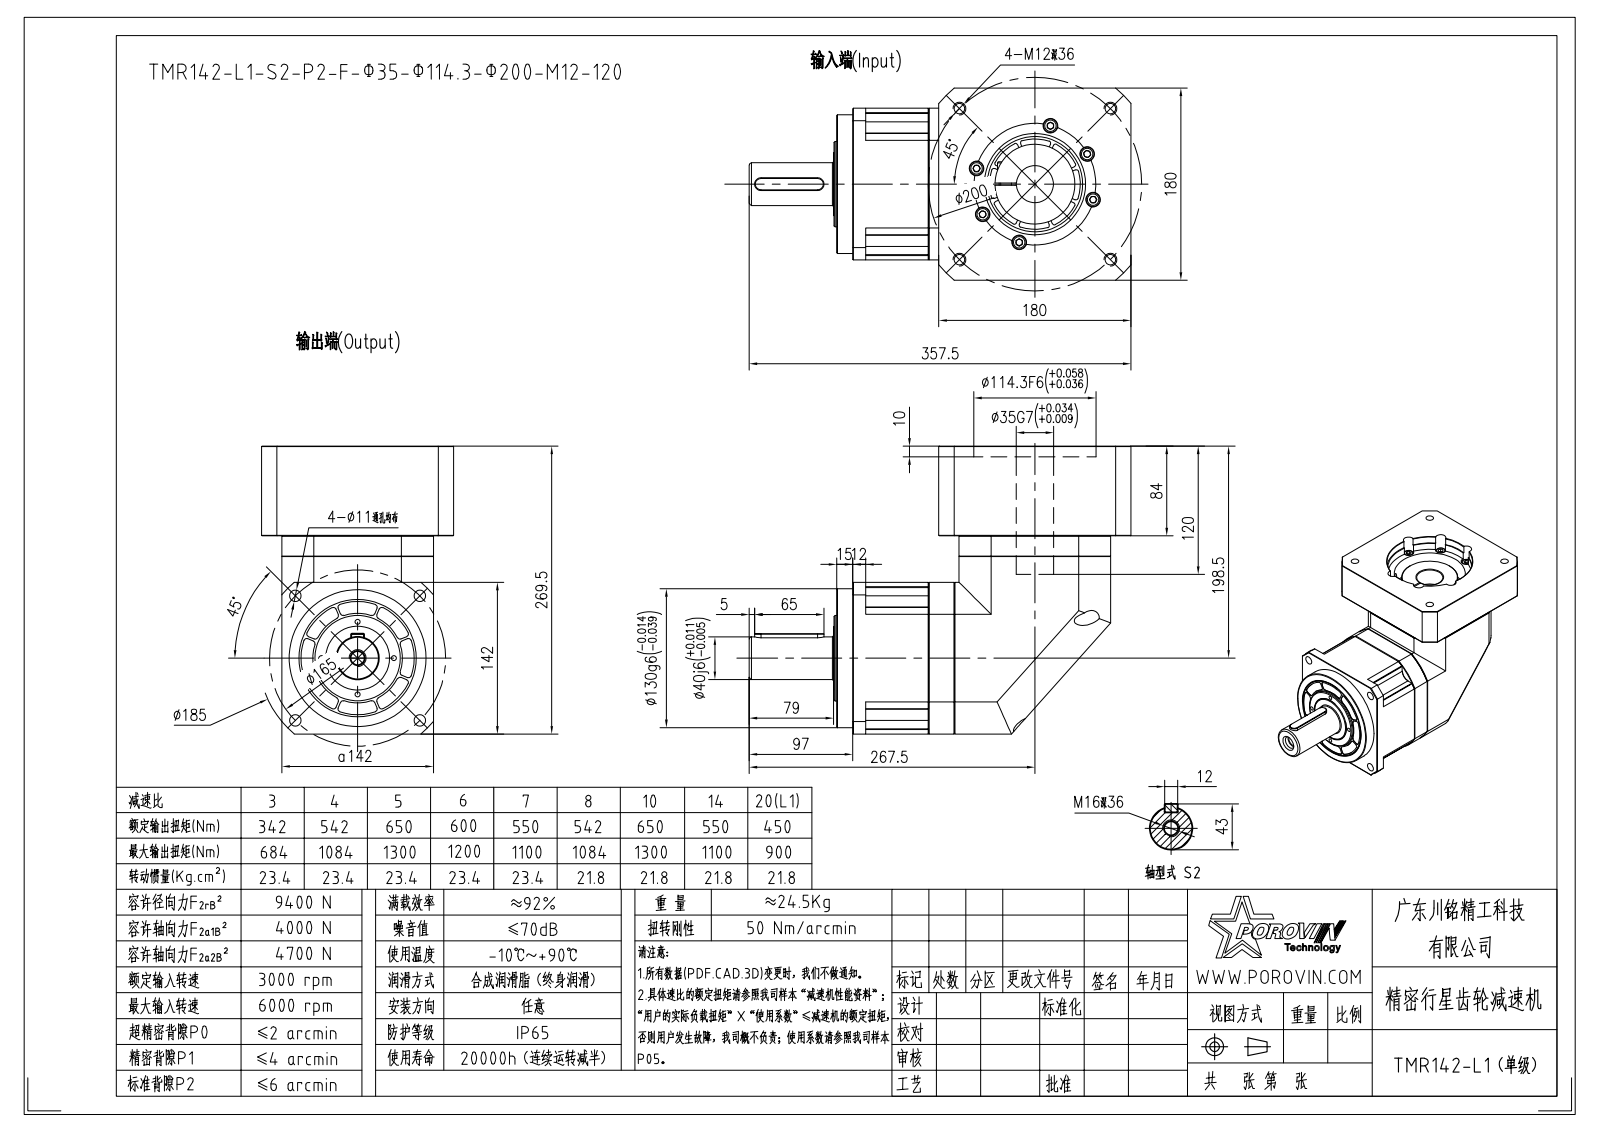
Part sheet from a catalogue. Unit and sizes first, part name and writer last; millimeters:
Units: millimetres
Overall size (bounding box): 357.5 × 269.5 × 180
Round holes (diameter × count): ⌀8.68 ×16, ⌀9 ×16, ⌀14 ×16, ⌀6.8 ×13, ⌀5 ×4, ⌀10.2 ×4, ⌀11 ×4, ⌀8.5 ×1, ⌀10.5 ×1, ⌀13.6 ×1, ⌀17 ×1, ⌀17.5 ×1
Round bosses / shafts (diameter × count): ⌀13 ×16, ⌀12.88 ×16, ⌀8 ×16, ⌀130 ×1, ⌀125 ×1, ⌀80 ×1, ⌀75 ×1, ⌀67 ×1
Partial cylindrical surfaces — rounded edges, fillets, slot ends (radius × count): R2 ×64, R1 ×20, R10.5 ×4, R6 ×3, R82 ×3, R42.5 ×2, R8.25 ×1, R50 ×1
Main face-to-face distances: 19, 161, 142, 24.5, 24.3, 19.5, 180, 103.5, 84, 15
Hole centre spacings: 56.5, 43.24, 62.84, 79.9, 104.39, 110.07, 21.17, 46.62
Volume: 6 796 000 mm³ · Surface area: 576 430 mm²
Bodies: 42 solids, 1353 faces (533 planar, 555 cylindrical, 265 other)
Part name (STEP PRODUCT): SPRING_LOCK_WASHERS--NORMAL_TYP; HEXAGON_SOCKET_HEAD_CAP_S-15493; HEXAGON_SOCKET_HEAD_CAP_S-24392; HEXAGON_SOCKET_HEAD_CAP_S-25544 (+8 more)
STEP written by: CREO PARAMETRIC BY PTC INC, 2020053 (CONFIG_CONTROL_DESIGN)
